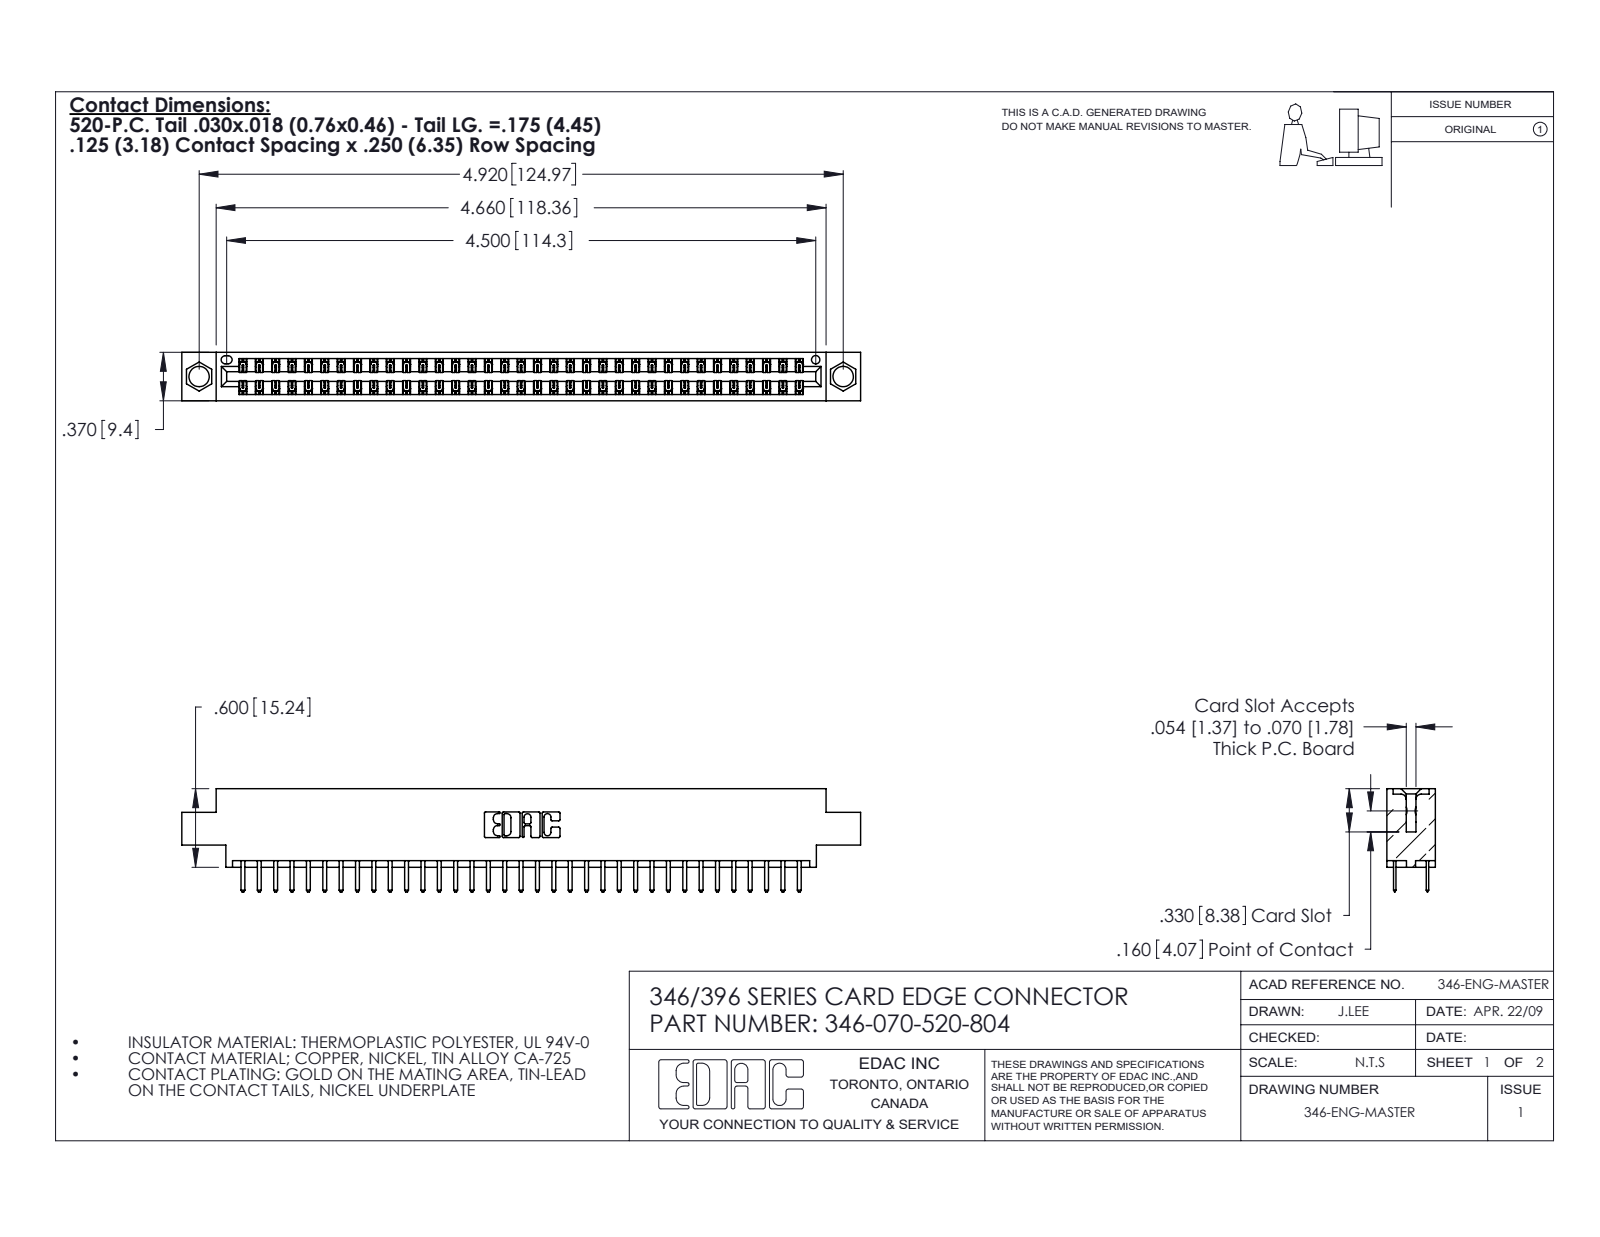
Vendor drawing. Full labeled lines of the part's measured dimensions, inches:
Part name (STEP PRODUCT): 346 Part_0.170 Offset - 0.156 Dia-TH; 345-292-001_345-293-120; 346-070-520-804
STEP written by: SolidWorks 2020 (CONFIG_CONTROL_DESIGN)
Units: inches
Bodies: 71 solids, 4060 faces (2684 planar, 1376 cylindrical, 0 other)
Overall size (bounding box): 5.185 × 0.788 × 0.37
Volume: 0.763 in³ · Surface area: 26.39 in²
Round holes (diameter × count): ⌀0.156 ×2, ⌀0.064 ×1
Partial cylindrical surfaces — rounded edges, fillets, slot ends (radius × count): R0.006 ×105, R0.01 ×74, R0.01 ×22, R0.007 ×6, R0.031 ×6, R0.026 ×3, R0.014 ×2, R0.022 ×2
Main face-to-face distances: 0.048, 0.322, 0.37, 0.25, 0.275, 0.072, 0.298, 0.025, 0.222, 0.148
Hole centre spacings: 0.246, 4.711, 4.92
